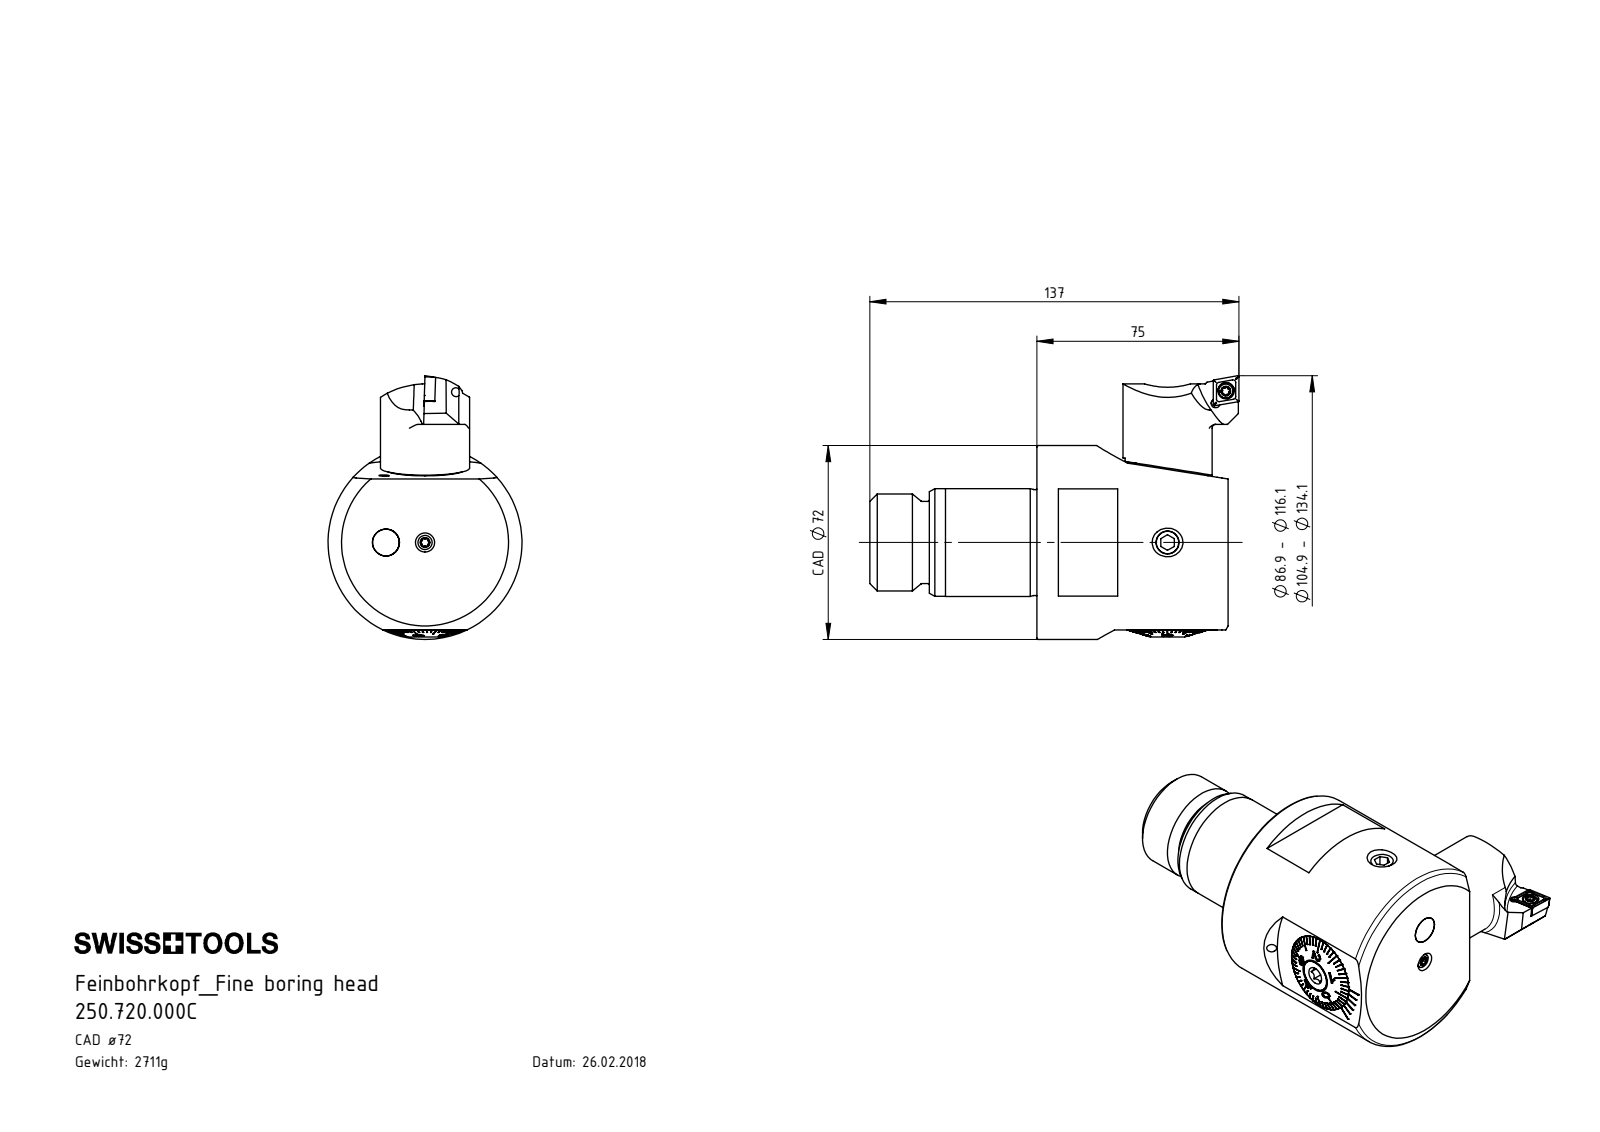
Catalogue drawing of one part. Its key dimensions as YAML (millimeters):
part_name: "F72-BG1.011.056; F72-BG2.015.020_B; 250.720.000C; CCMT09T304 (+8 more)"
step_written_by: "SolidWorks 2017 (CONFIG_CONTROL_DESIGN)"
units: millimeters
bodies: {solids: 15, faces: 817, planar: 322, cylindrical: 169, other: 326}
overall_size: [137, 97.89, 72]
volume: 345734
surface_area: 65650
round_holes:
  - {diameter: 3.3, count: 9}
  - {diameter: 8.5, count: 3}
  - {diameter: 4.2, count: 1}
  - {diameter: 4.4, count: 1}
  - {diameter: 6.1, count: 1}
  - {diameter: 8, count: 1}
  - {diameter: 10, count: 1}
  - {diameter: 11, count: 1}
  - {diameter: 11.75, count: 1}
  - {diameter: 12, count: 1}
  - {diameter: 12.4, count: 1}
  - {diameter: 13, count: 1}
round_bosses_or_shafts:
  - {diameter: 5.25, count: 2}
  - {diameter: 4, count: 2}
  - {diameter: 72, count: 1}
  - {diameter: 40, count: 1}
  - {diameter: 39.95, count: 1}
  - {diameter: 39.3, count: 1}
  - {diameter: 36, count: 1}
  - {diameter: 33.1, count: 1}
partial_cylinders:
  - {radius: 0.34, count: 12}
  - {radius: 0.59, count: 12}
  - {radius: 1, count: 5}
  - {radius: 3.2, count: 3}
  - {radius: 0.5, count: 2}
  - {radius: 3.5, count: 1}
  - {radius: 8, count: 1}
  - {radius: 30, count: 1}
face_to_face_distances: [71, 60, 55.8, 62, 133, 62.28, 6.48, 2.5, 61.1, 5.3]
hole_center_spacings: [5.94, 6.09, 14.05, 14.5, 26, 32.5]
